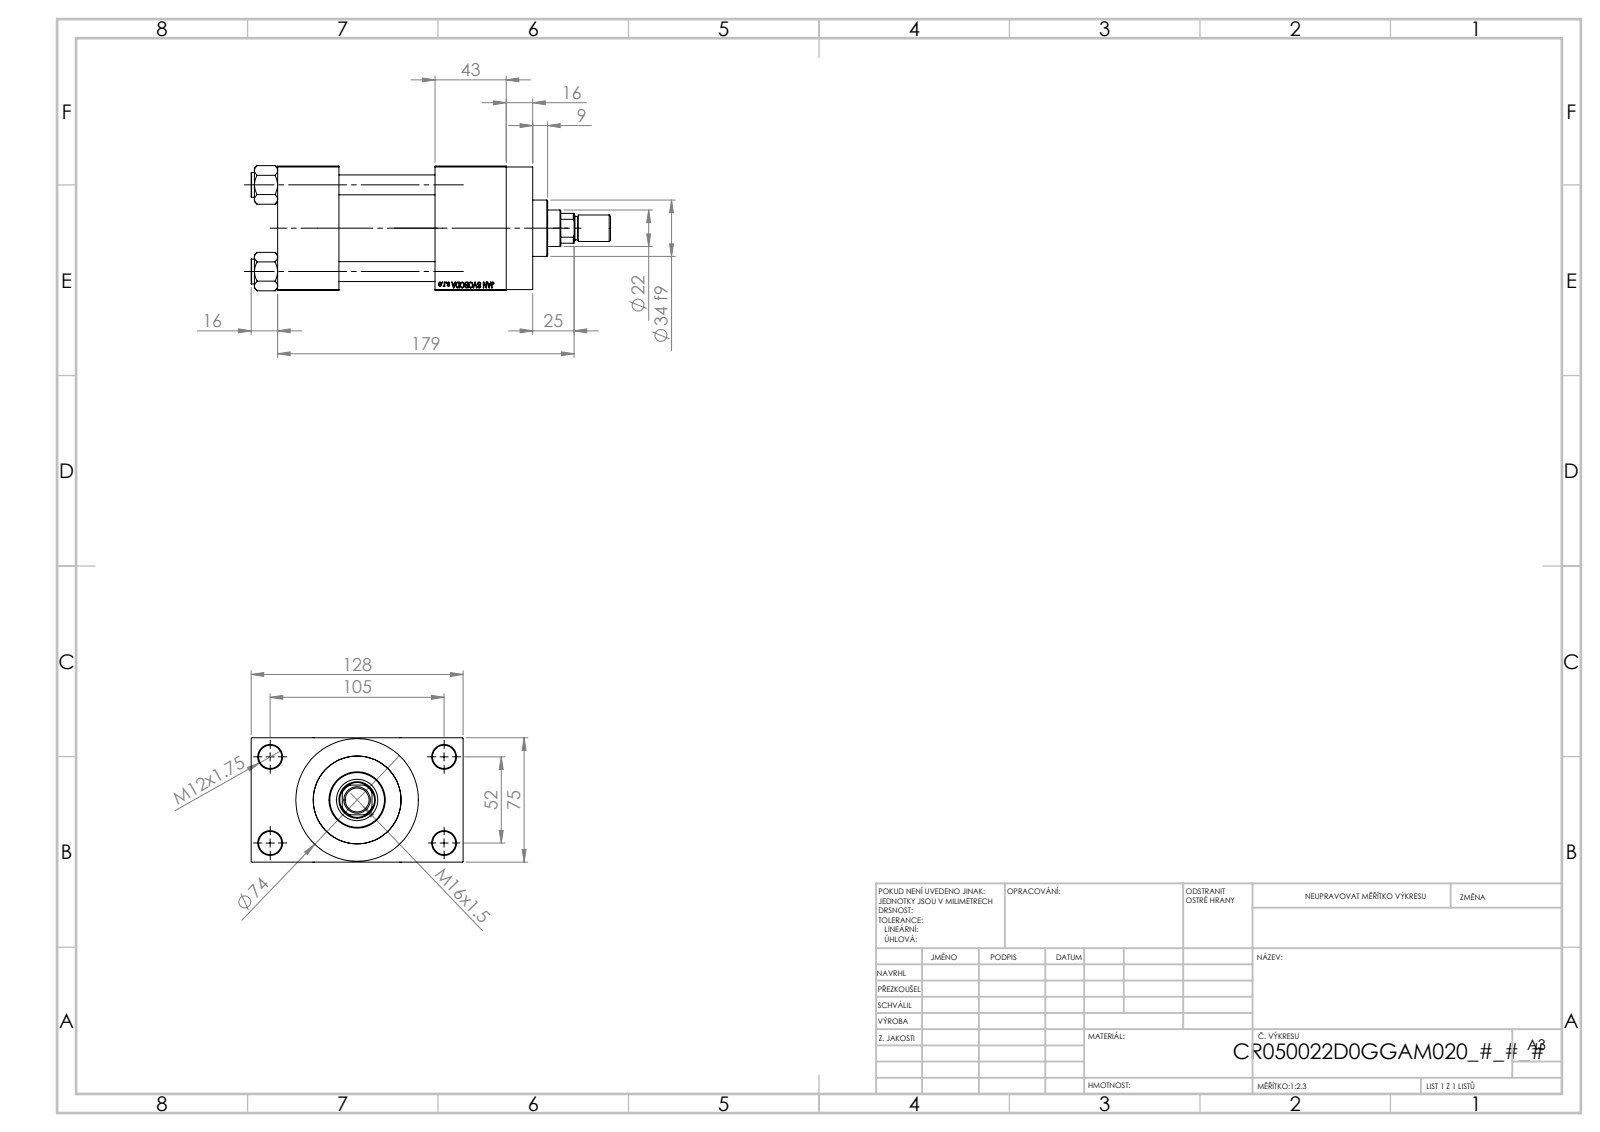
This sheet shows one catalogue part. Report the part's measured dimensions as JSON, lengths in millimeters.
{"part_name": "ROD_END_AH; V215CR_D_Body; V215CR_VCP_D; V215_VC_A (+2 more)", "step_written_by": "SolidWorks 2019 (CONFIG_CONTROL_DESIGN)", "units": "millimeters", "bodies": {"solids": 12, "faces": 1118, "planar": 501, "cylindrical": 93, "other": 524}, "overall_size": [217, 128, 75.54], "volume_mm3": 810849, "surface_area_mm2": 166488, "round_holes": [[12, 4], [14, 4], [7, 2], [20.96, 2], [30, 2], [10.5, 1], [22, 1], [25, 1], [41, 1], [50, 1], [53, 1]], "round_bosses_or_shafts": [[15, 4], [74, 1], [56, 1], [34, 1], [16, 1], [14, 1]], "partial_cylinders_radius": [[10.5, 1]], "face_to_face_distances": [75, 58, 37, 95, 26.5, 101.5, 138, 101, 43, 16], "hole_center_spacings": [26.35, 36.98, 52.3, 58.43, 58.59, 78.65, 94.37, 52]}
